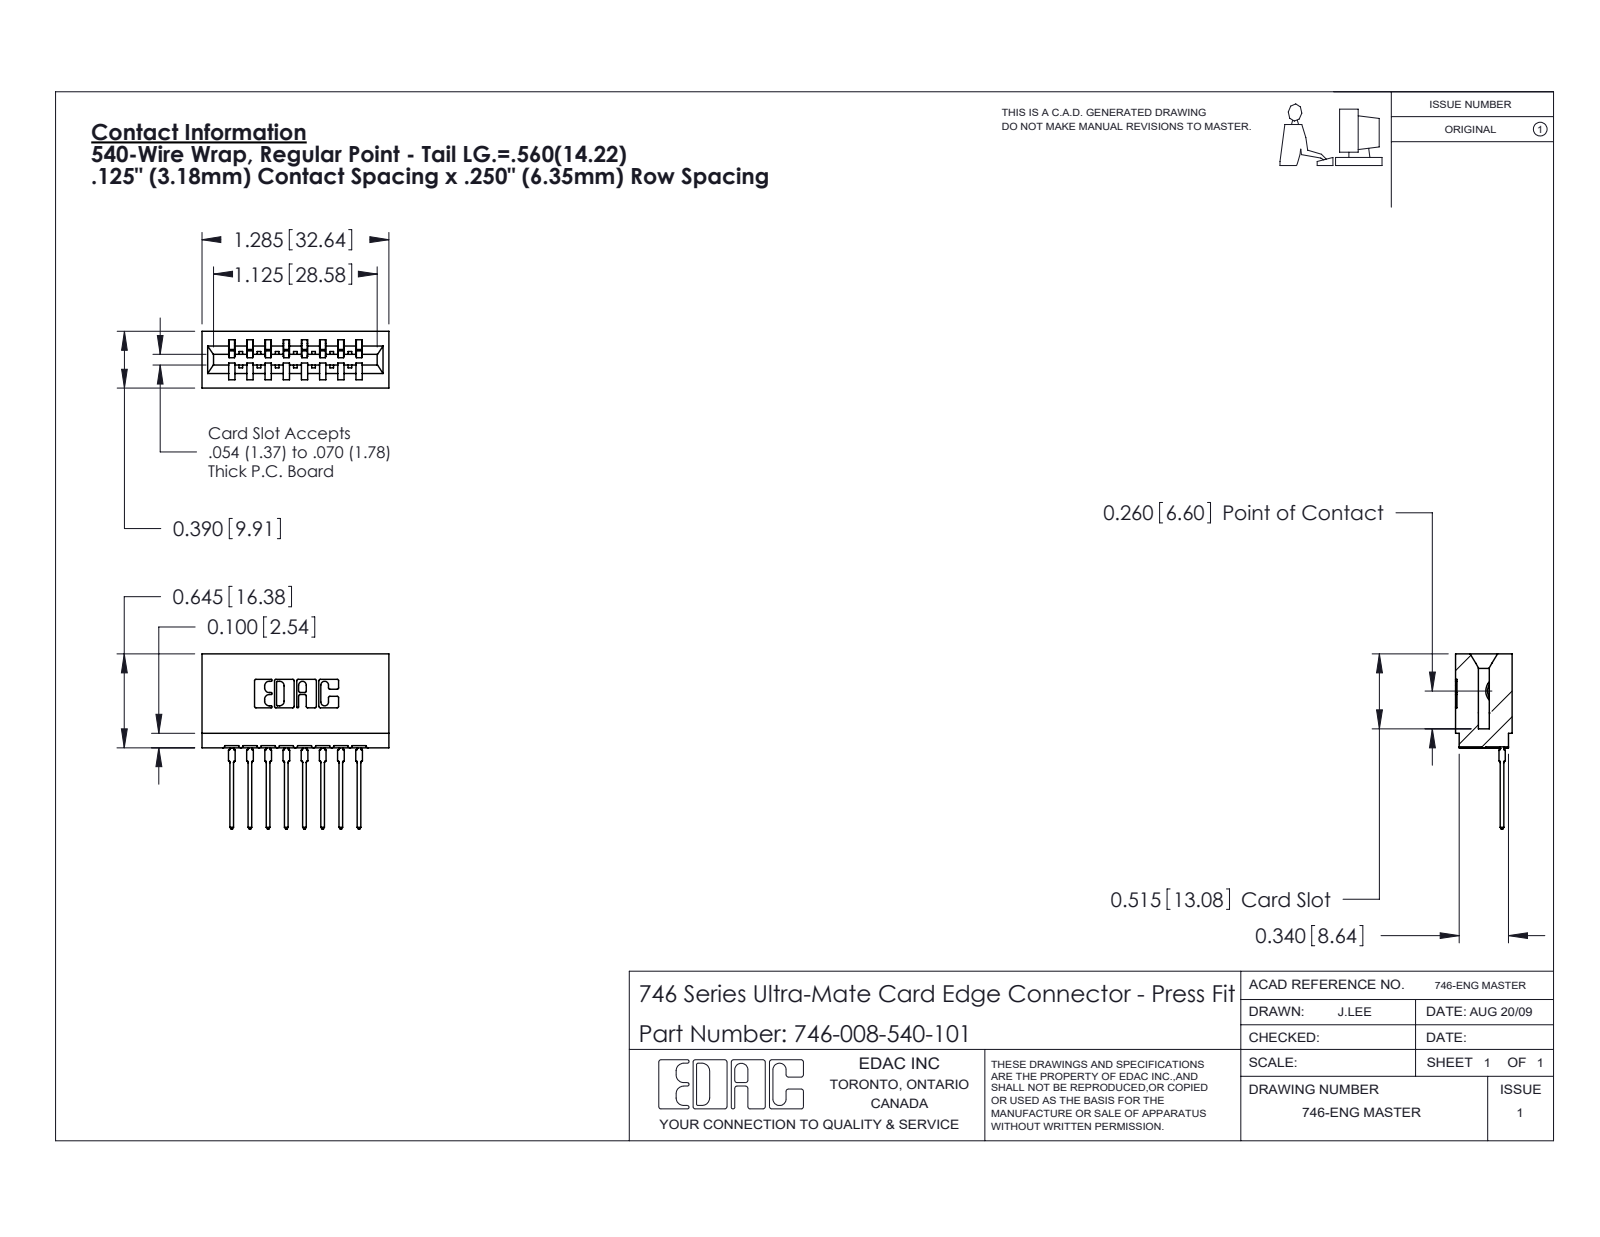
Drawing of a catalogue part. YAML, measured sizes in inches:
part_name: "746-008-540-101; 746 Part_.515 Slot Depth - 01; 746-292-001_540"
step_written_by: "SolidWorks 2020 (CONFIG_CONTROL_DESIGN)"
units: inches
bodies: {solids: 9, faces: 961, planar: 559, cylindrical: 194, other: 208}
overall_size: [1.285, 1.204, 0.39]
volume: 0.224
surface_area: 7.674
partial_cylinders:
  - {radius: 0.01, count: 22}
  - {radius: 0.021, count: 16}
  - {radius: 0.015, count: 9}
  - {radius: 0.007, count: 6}
  - {radius: 0.031, count: 6}
  - {radius: 0.005, count: 4}
  - {radius: 0.011, count: 4}
  - {radius: 0.026, count: 3}
face_to_face_distances: [0.25, 0.042, 0.125, 0.5, 0.333, 0.057, 0.292, 0.208, 0.375, 0.125]
